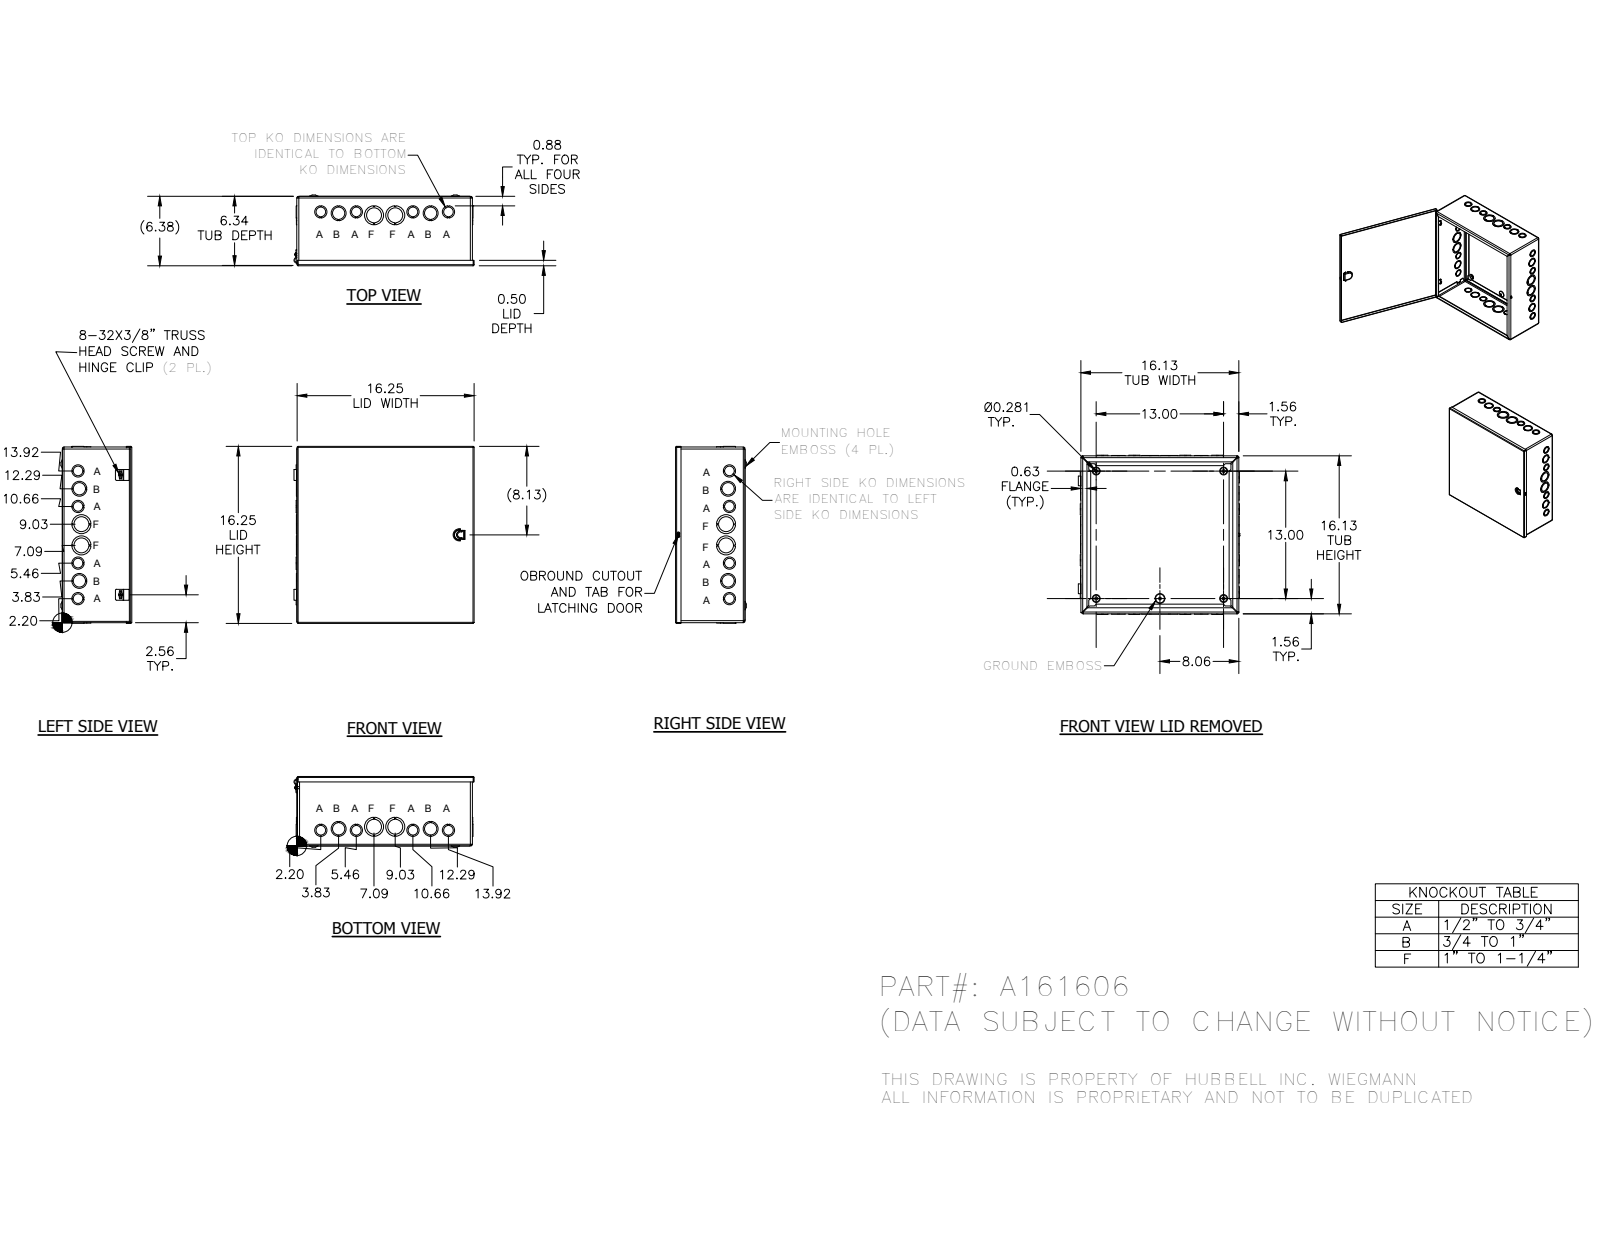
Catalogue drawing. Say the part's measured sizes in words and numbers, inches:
The part is named "A1616BA; A161606WRA; 31816; 372177 (+3 more)". Its 3-D file was written by "Autodesk Inventor 2014 (AUTOMOTIVE_DESIGN)". It is 39 solids with 1391 faces: 934 planar, 299 cylindrical and 158 other. Overall it measures 16.637 by 16.437 by 6.504 inches. Round holes: 12 of diameter 1.125, 8 of diameter 0.875, 8 of diameter 1.375, 4 of diameter 0.3, 4 of diameter 1.75, 2 of diameter 0.14, 1 of diameter 0.165. Round bosses or shafts: 2 of diameter 0.384, 2 of diameter 0.164, 1 of diameter 0.228. Partial cylindrical surfaces (rounded edges, fillets, slot ends): 15 of radius 0.125, 10 of radius 0.031, 9 of radius 0.063, 8 of radius 0.094, 8 of radius 0.187, 4 of radius 0.055, 4 of radius 0.062, 4 of radius 0.07. The main face-to-face distances are 0.062, 0.062, 16.063, 6.316, 6.254, 0.063, 6.317, 6.379, 16.001, 16.125. The hole center spacings are 1.635, 1.659, 3.265, 3.584, 5.204, 6.831, 8.46, 13.
